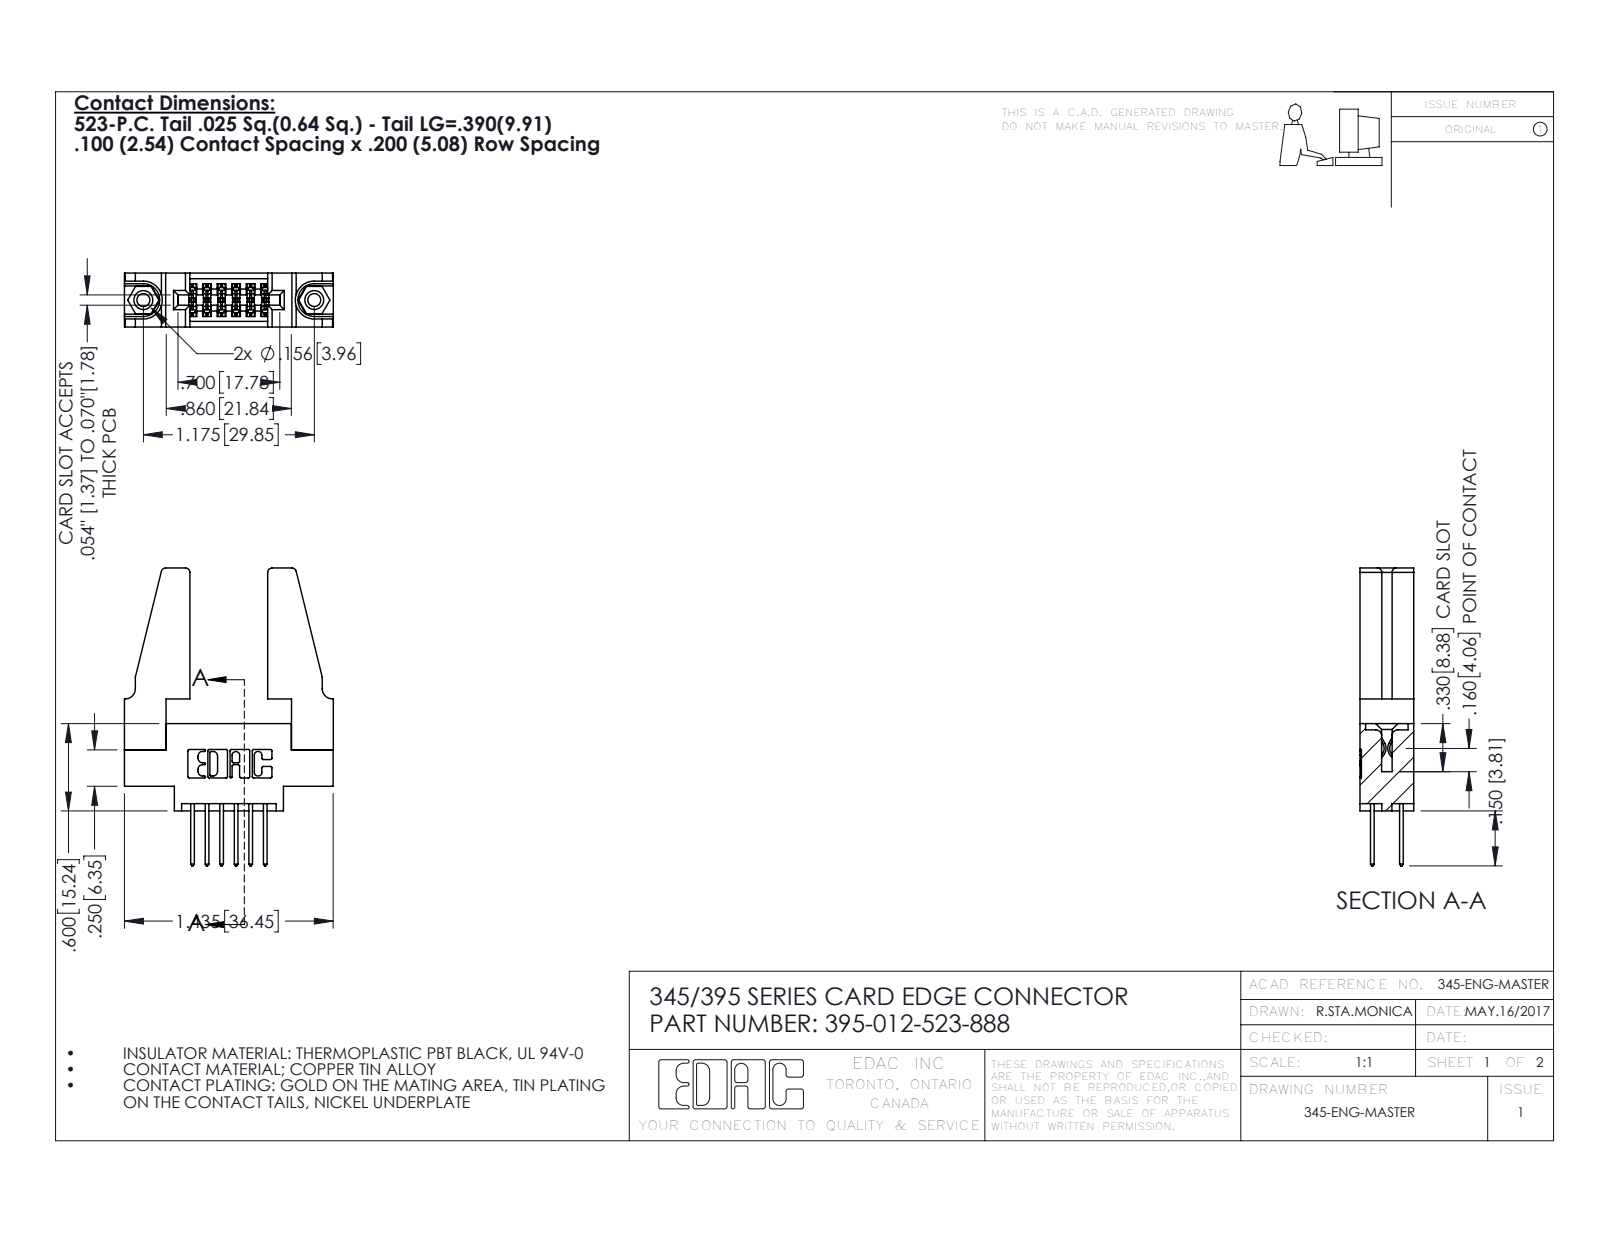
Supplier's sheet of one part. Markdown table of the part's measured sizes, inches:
| quantity | value |
| --- | --- |
| part name | 345 Part_0.170 Offset - 0.156 Dia-TH; 345-220-078_345-220-088; 395-012-523-888; 345-292-001_345-293-123 (+1 more) |
| STEP written by | SolidWorks 2016 (CONFIG_CONTROL_DESIGN) |
| units | inches |
| bodies | 17 solids, 854 faces (552 planar, 286 cylindrical, 16 other) |
| overall size | 2.047 × 1.436 × 0.37 |
| volume | 0.389 in³ |
| surface area | 11.3 in² |
| round holes (diameter × count) | 0.089 × 2, 0.125 × 2, 0.156 × 2, 0.064 × 1 |
| round bosses / shafts (diameter × count) | 0.155 × 2 |
| partial cylindrical surfaces (radius × count) | 0.01 × 22, 0.006 × 18, 0.01 × 12, 0.03 × 8, 0.007 × 6, 0.031 × 6, 0.026 × 3, 0.014 × 2 |
| main face-to-face distances | 0.37, 0.072, 0.298, 0.2, 0.098, 0.272, 0.025, 0.225, 0.15, 0.148 |
| hole center spacings | 0.27, 0.946, 1.175 |
